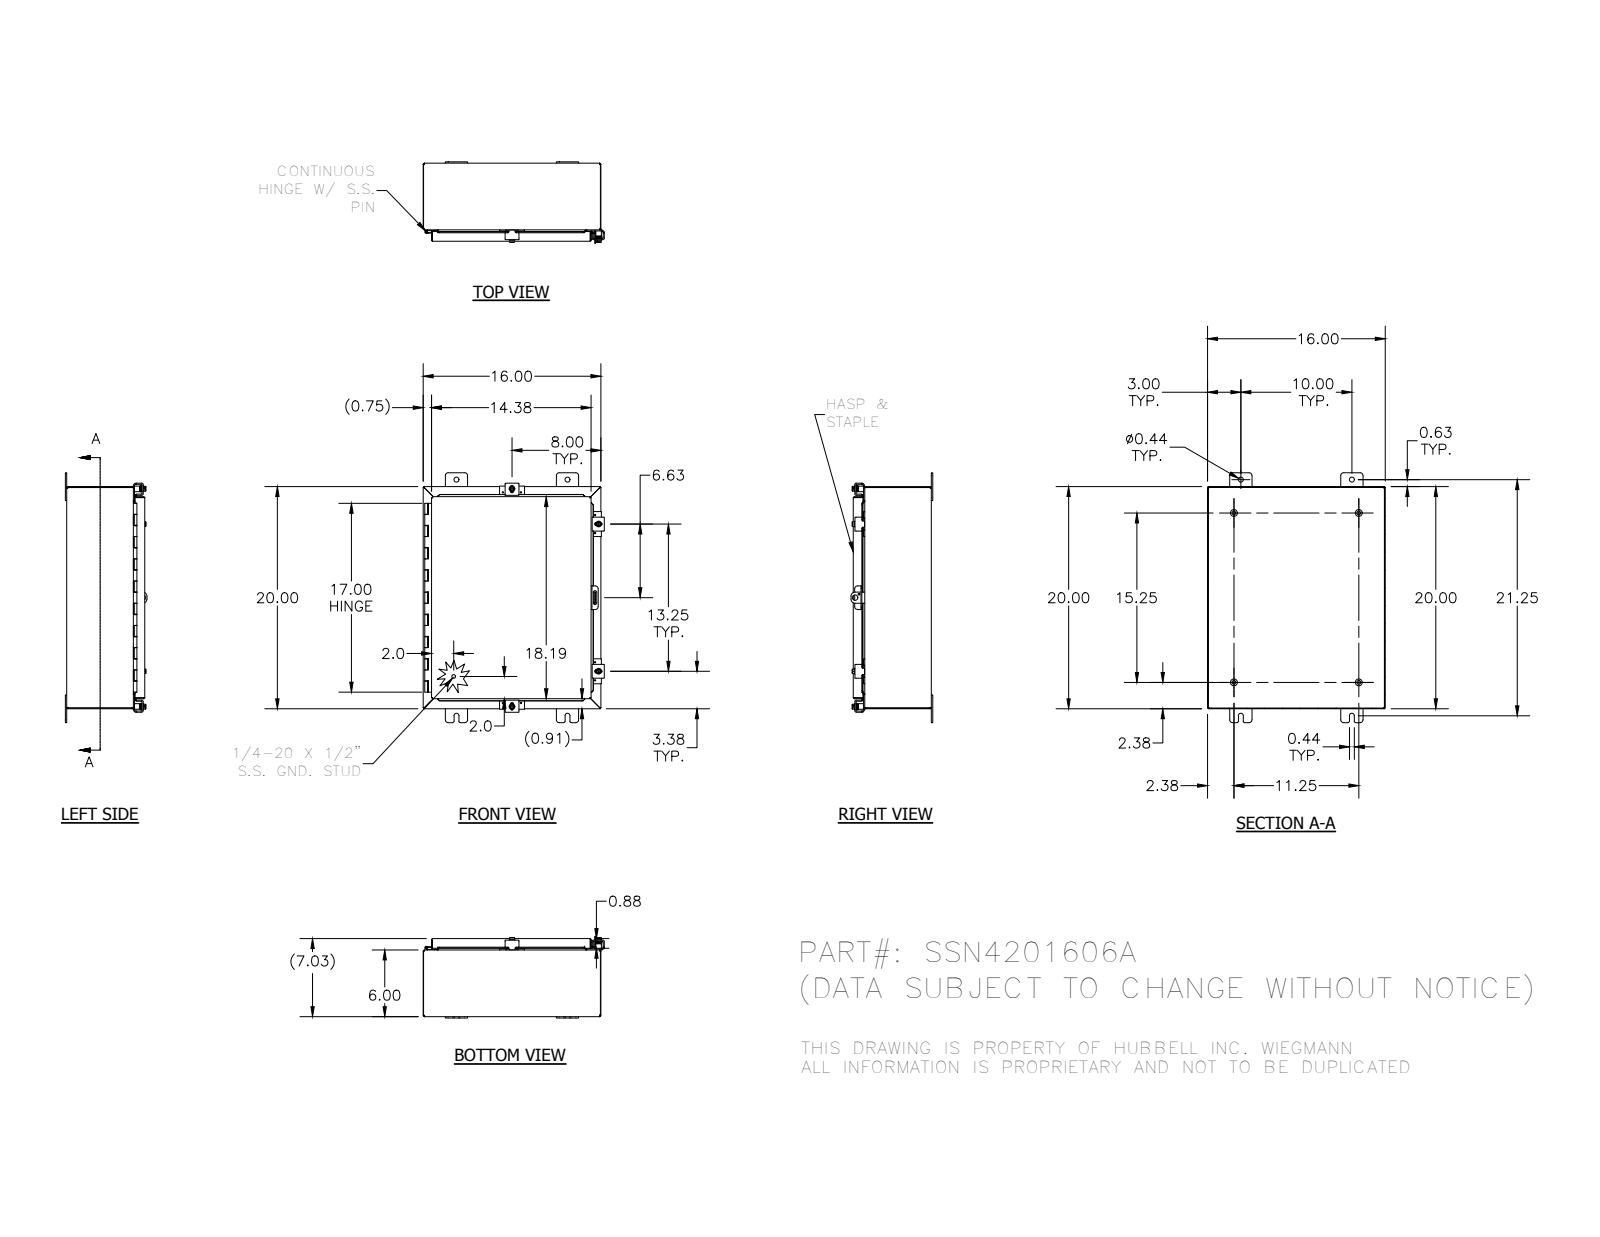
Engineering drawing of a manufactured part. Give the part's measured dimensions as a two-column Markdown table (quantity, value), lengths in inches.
| quantity | value |
| --- | --- |
| part name | SSN4201606A; 30818; 30824-1; SSN42016ALID (+8 more) |
| STEP written by | SolidWorks 2014 (AUTOMOTIVE_DESIGN) |
| units | inches |
| bodies | 37 solids, 1428 faces (575 planar, 612 cylindrical, 241 other) |
| overall size | 22.5 × 16.216 × 7.355 |
| volume | 103.8 in³ |
| surface area | 2 700 in² |
| round holes (diameter × count) | 0.11 × 8, 0.211 × 4, 0.281 × 4, 0.3 × 4, 0.438 × 4, 0.125 × 1, 0.156 × 1, 0.5 × 1 |
| round bosses / shafts (diameter × count) | 0.25 × 6, 0.625 × 4, 0.52 × 4, 0.5 × 4, 0.35 × 4, 0.33 × 4, 0.337 × 1, 0.12 × 1 |
| partial cylindrical surfaces (radius × count) | 0.03 × 49, 0.125 × 33, 0.25 × 29, 0.031 × 23, 0.105 × 23, 0.062 × 14, 0.07 × 8, 0.141 × 8 |
| main face-to-face distances | 0.074, 6.959, 6.885, 7.033, 15.926, 19.926, 5.926, 1.033, 16, 15.852 |
| hole center spacings | 0.876, 19.306, 13.25, 0.876, 1.625, 1.625, 4.189, 4.341 |
